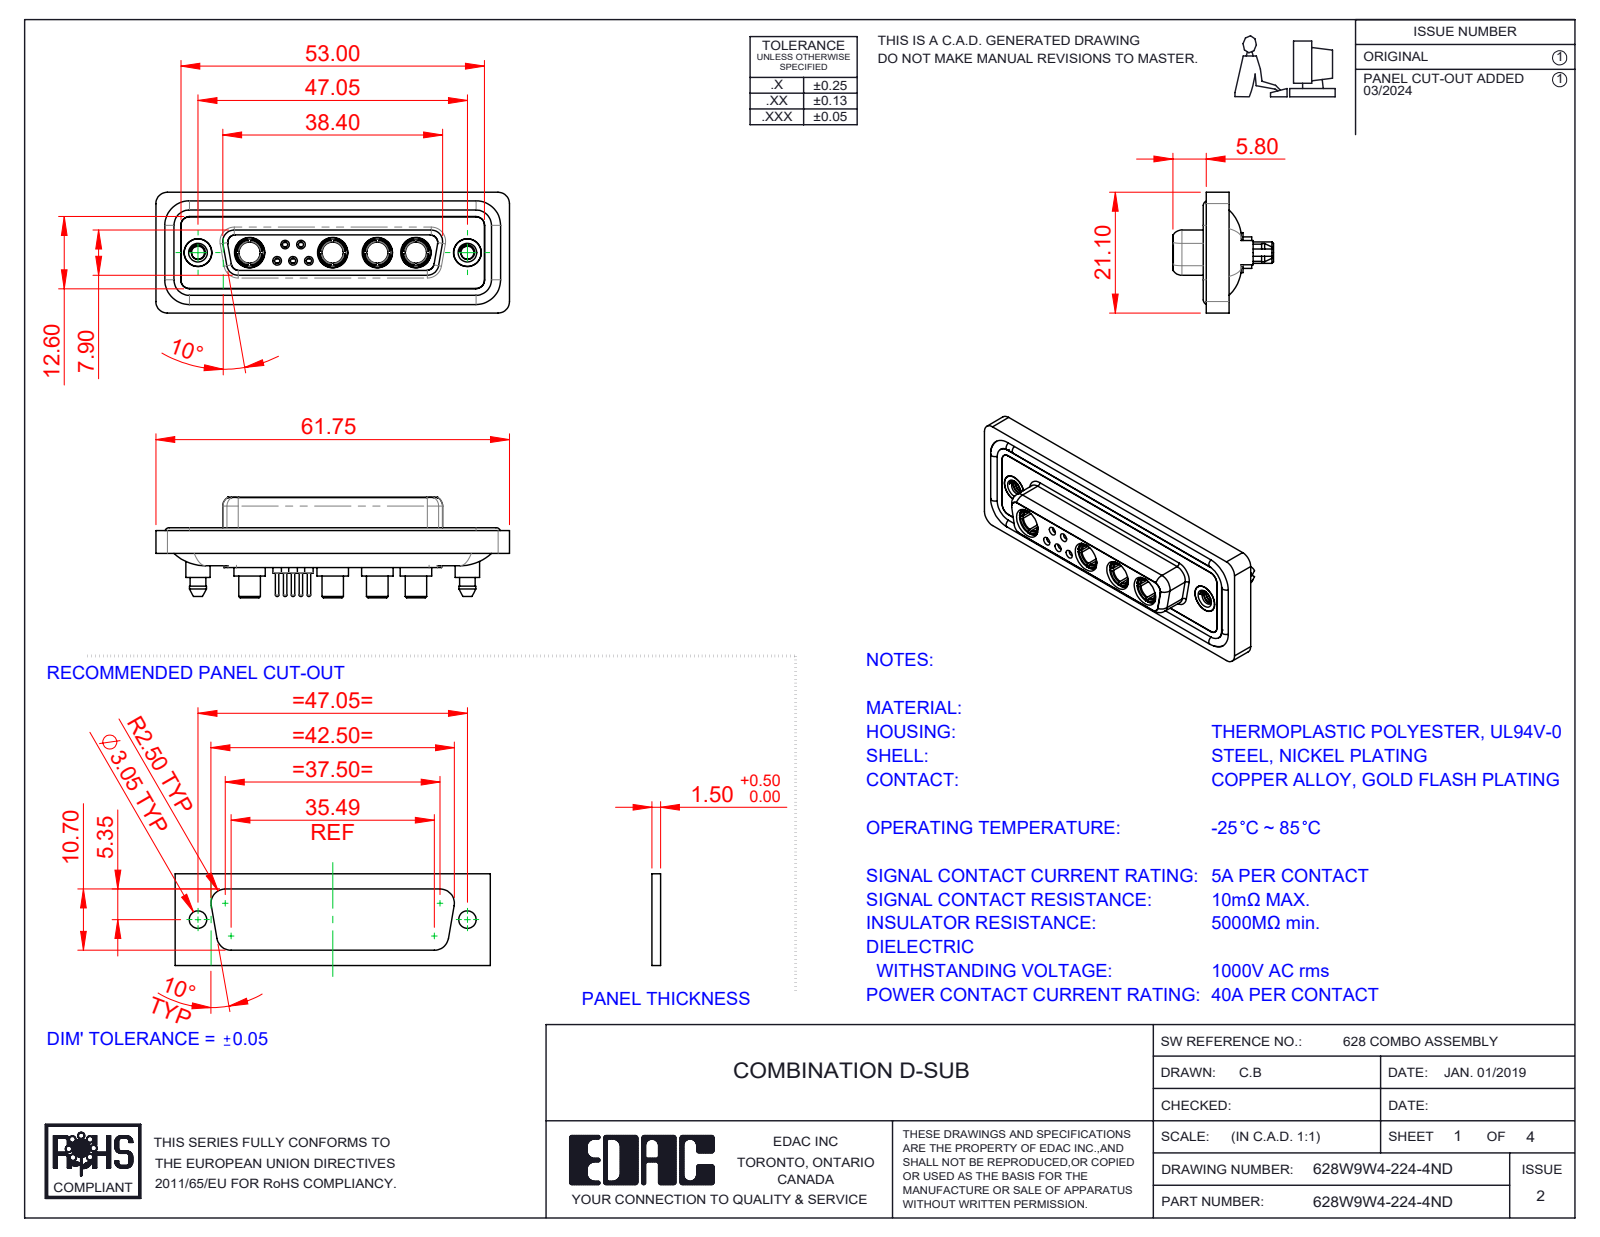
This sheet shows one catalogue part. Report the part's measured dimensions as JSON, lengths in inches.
{"part_name": "628Combo Shell Front_25 Contacts; 628Combo Contact Row 1_24; 628Combo Contact Row 2_24; 628Combo Waterproof Housing_25 Contacts (+5 more)", "step_written_by": "SolidWorks 2023 (CONFIG_CONTROL_DESIGN)", "units": "inches", "bodies": {"solids": 20, "faces": 1023, "planar": 312, "cylindrical": 423, "other": 288}, "overall_size": [2.431, 0.831, 0.691], "volume_in3": 0.515, "surface_area_in2": 21.61, "round_holes": [[0.191, 6], [0.035, 5], [0.043, 5], [0.059, 5], [0.079, 5], [0.146, 4], [0.209, 4], [0.063, 3], [0.067, 2], [0.089, 2], [0.157, 2], [0.159, 2]], "round_bosses_or_shafts": [[0.063, 6], [0.087, 5], [0.024, 5], [0.217, 4], [0.205, 4], [0.195, 4], [0.187, 4], [0.148, 4]], "partial_cylinders_radius": [[0.059, 24], [0.079, 18], [0.063, 10], [0.053, 8], [0.01, 4], [0.02, 4], [0.024, 4], [0.026, 4]], "face_to_face_distances": [0.016, 0.071, 0.293, 0.222, 0.02, 0.278, 0.26, 0.063, 0.043, 0.114], "hole_center_spacings": [0.124, 0.109, 0.198, 0.109, 0.173, 0.198, 0.218, 0.226]}
